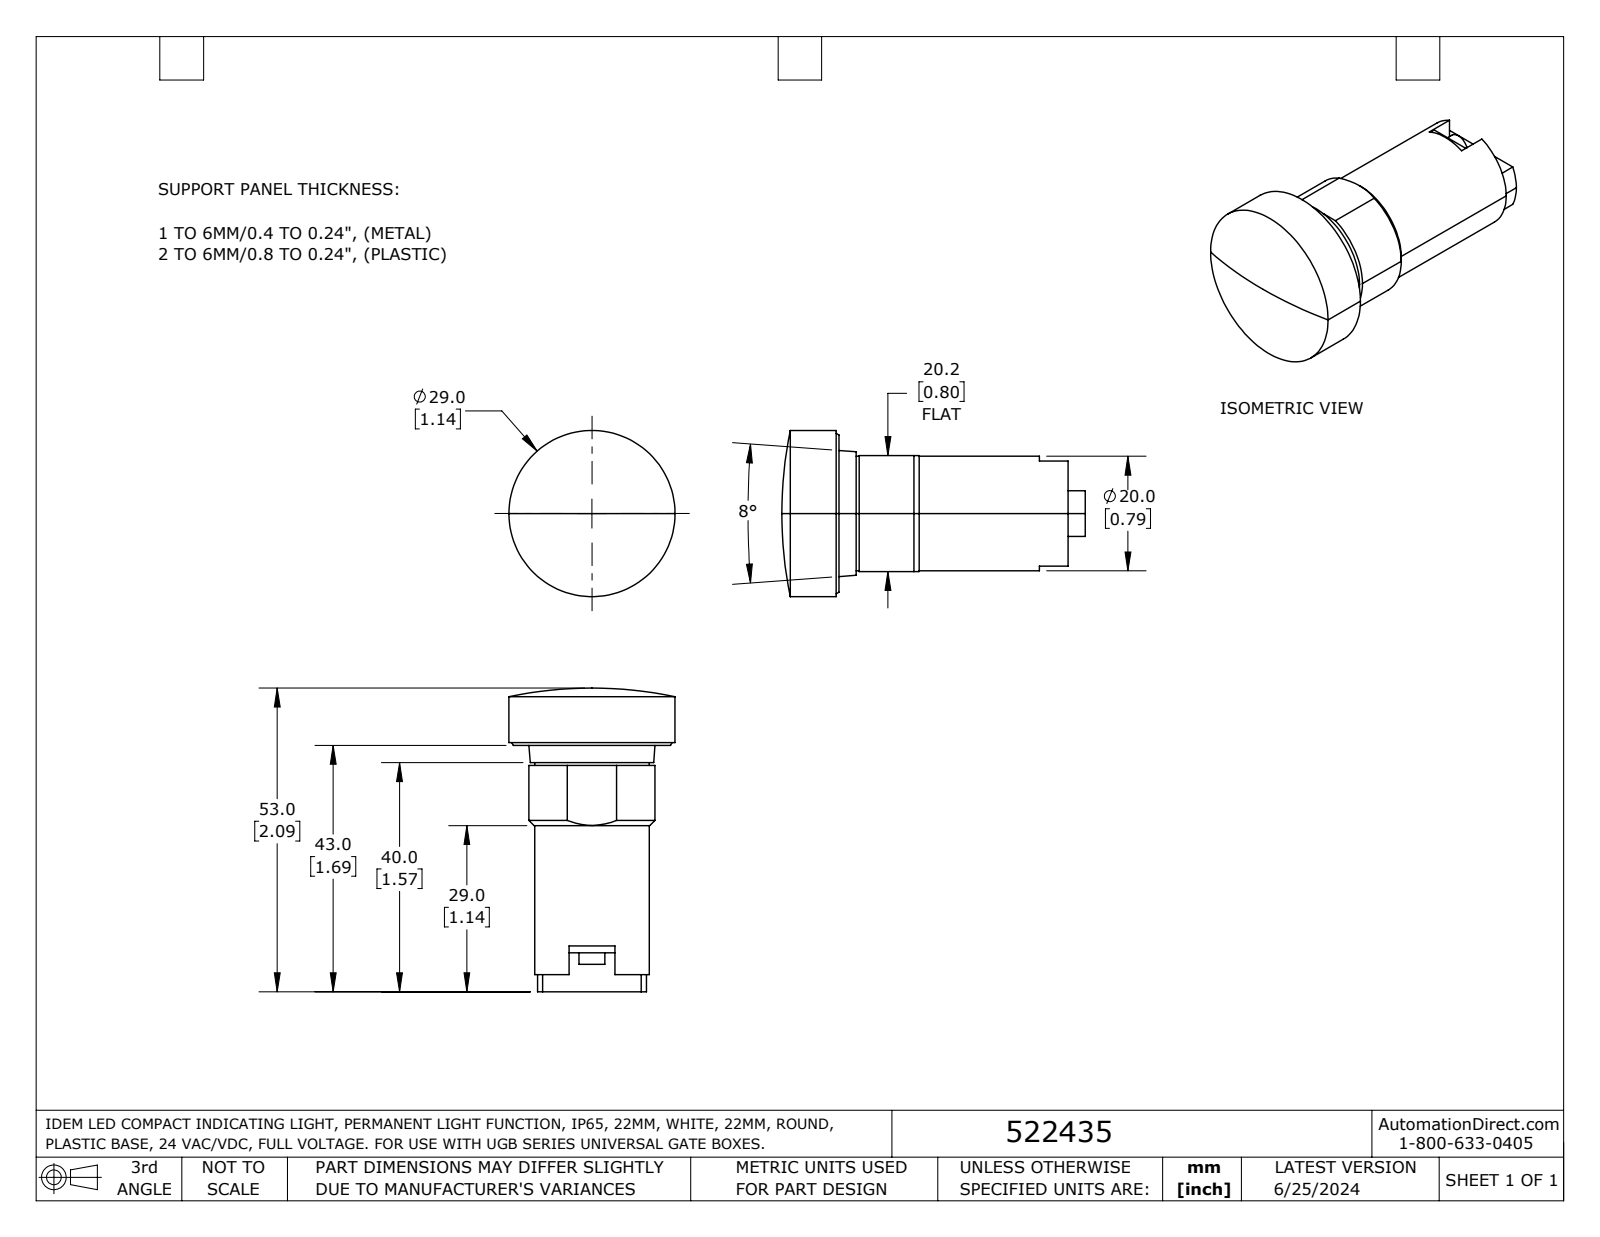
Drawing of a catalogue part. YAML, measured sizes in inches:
part_name: "522435"
step_written_by: "SolidWorks 2023 (AUTOMOTIVE_DESIGN)"
units: inches
bodies: {solids: 1, faces: 50, planar: 24, cylindrical: 18, other: 8}
overall_size: [2.087, 1.142, 1.142]
volume: 1.192
surface_area: 7.789
round_bosses_or_shafts:
  - {diameter: 0.177, count: 2}
  - {diameter: 1.142, count: 1}
  - {diameter: 0.787, count: 1}
partial_cylinders:
  - {radius: 0.374, count: 1}
  - {radius: 0.433, count: 1}
face_to_face_distances: [0.241, 0.556, 1.693, 0.315, 0.118, 1.575, 0.138, 0.02, 0.797, 1.437]
